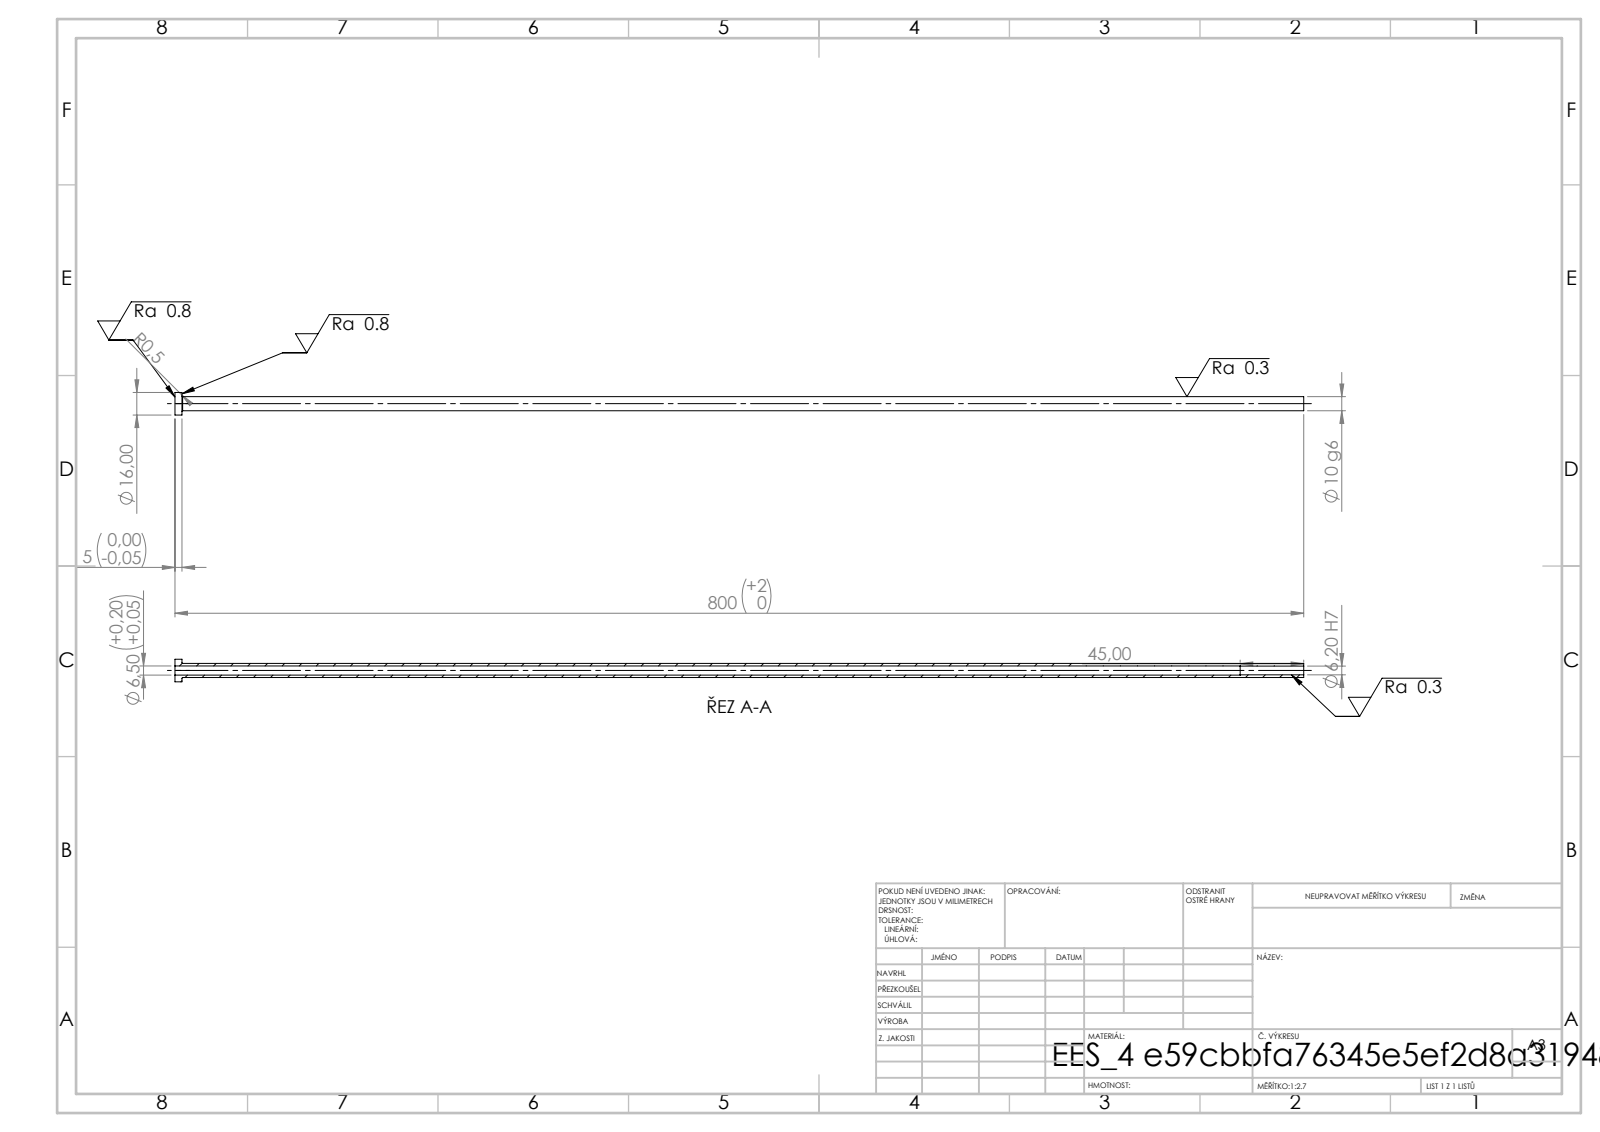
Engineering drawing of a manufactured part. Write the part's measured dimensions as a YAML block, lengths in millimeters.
step_written_by: "SolidWorks 2019 (CONFIG_CONTROL_DESIGN)"
units: millimeters
bodies: {solids: 1, faces: 14, planar: 4, cylindrical: 8, other: 2}
overall_size: [800, 16, 16]
volume: 37034
surface_area: 41856
round_holes:
  - {diameter: 6.2, count: 1}
  - {diameter: 6.5, count: 1}
round_bosses_or_shafts:
  - {diameter: 16, count: 1}
  - {diameter: 10, count: 1}
face_to_face_distances: [5, 800, 795, 755, 750, 45]
